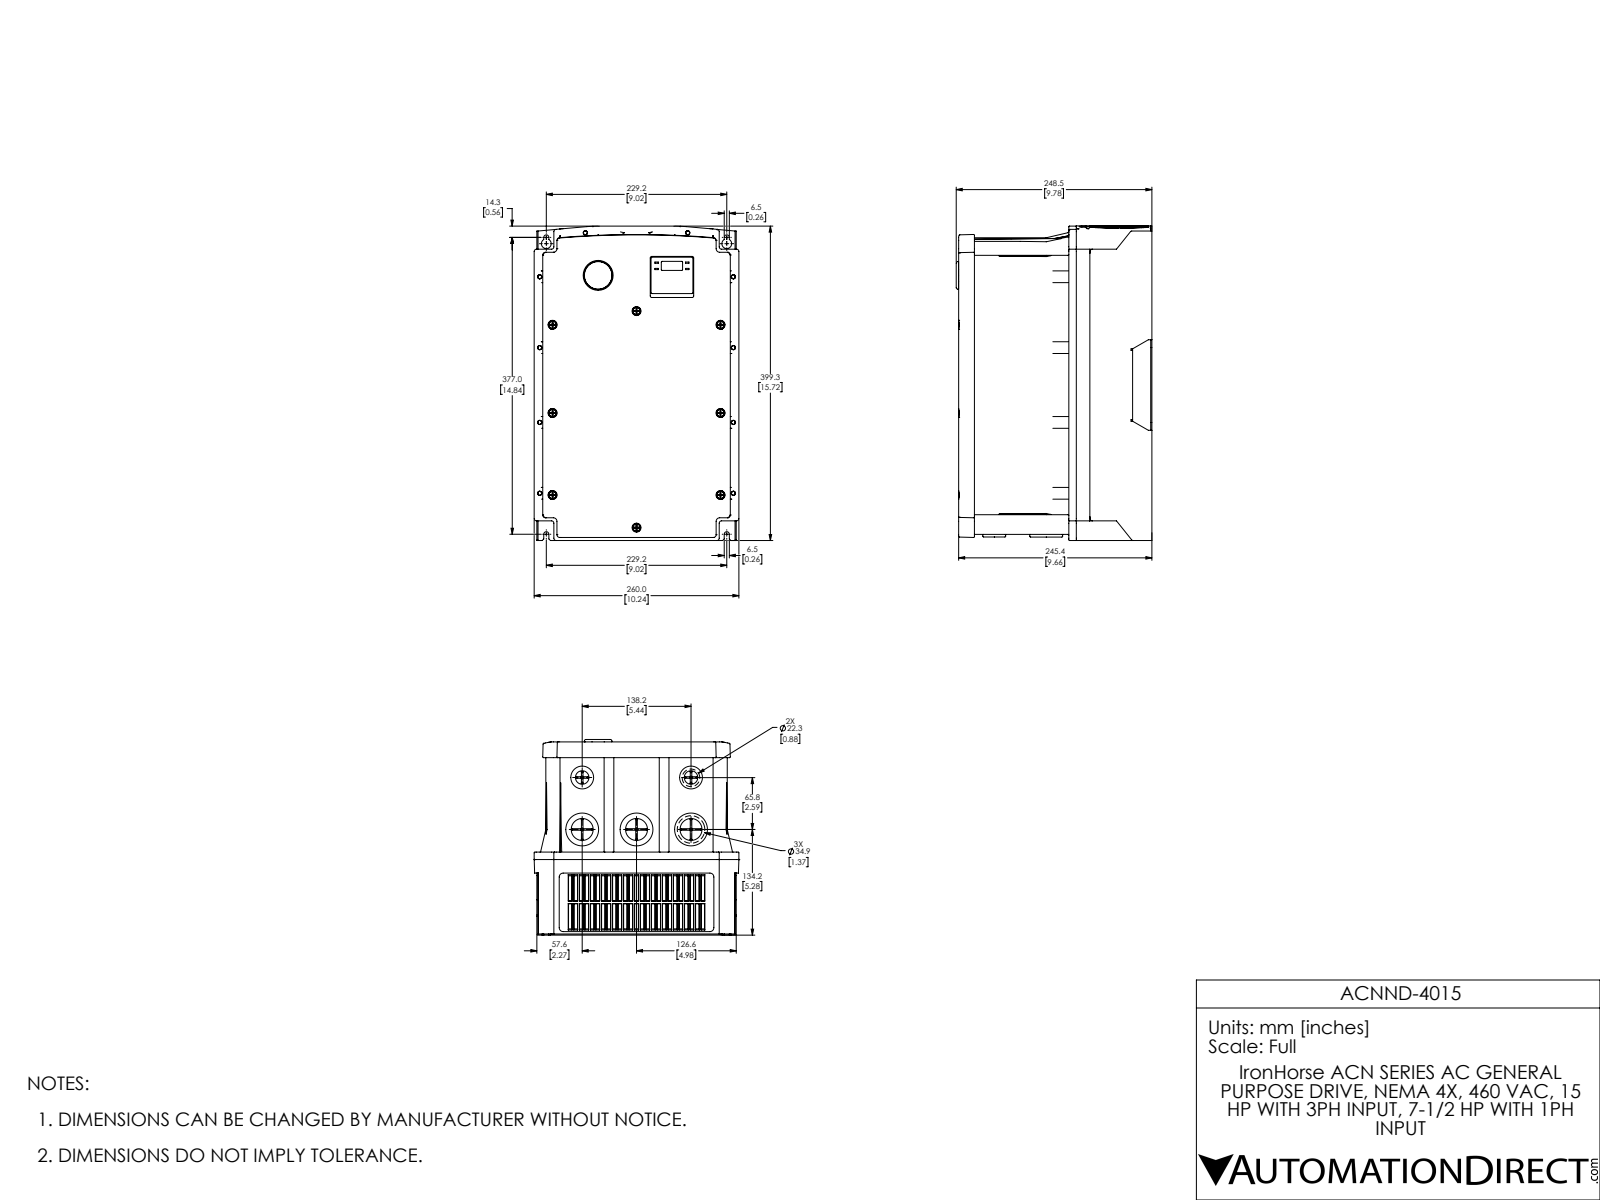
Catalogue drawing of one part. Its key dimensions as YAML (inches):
part_name: "total_s100_ip66_110_150_v3_asm red 1ext RED2 NEW1b2 COMPLETE EXT2F2 fill WITH NONPDS KNOB cmb3b sm2 cmb r1"
step_written_by: "SolidWorks 2017 (AUTOMOTIVE_DESIGN)"
units: inches
bodies: {solids: 2, faces: 5255, planar: 2354, cylindrical: 1370, other: 1531}
overall_size: [15.732, 10.236, 9.783]
volume: 1323
surface_area: 1378
round_holes:
  - {diameter: 0.217, count: 12}
  - {diameter: 0.197, count: 11}
  - {diameter: 0.409, count: 8}
  - {diameter: 1.098, count: 3}
  - {diameter: 1.524, count: 3}
  - {diameter: 0.492, count: 2}
  - {diameter: 0.677, count: 2}
  - {diameter: 0.878, count: 2}
  - {diameter: 1.024, count: 2}
  - {diameter: 1.181, count: 2}
  - {diameter: 1.772, count: 2}
  - {diameter: 2.362, count: 2}
round_bosses_or_shafts:
  - {diameter: 0.394, count: 8}
  - {diameter: 1.642, count: 3}
  - {diameter: 1.35, count: 3}
  - {diameter: 2.559, count: 2}
  - {diameter: 1.969, count: 2}
  - {diameter: 1.378, count: 2}
  - {diameter: 1.142, count: 2}
  - {diameter: 0.85, count: 2}
partial_cylinders:
  - {radius: 0.039, count: 127}
  - {radius: 0.012, count: 91}
  - {radius: 0.02, count: 85}
  - {radius: 0.008, count: 65}
  - {radius: 0.031, count: 36}
  - {radius: 0.118, count: 34}
  - {radius: 0.197, count: 25}
  - {radius: 0.157, count: 20}
face_to_face_distances: [0.059, 9.661, 9.461, 0.449, 9.52, 9.909, 0.39, 9.602, 9.071, 9.85]
hole_center_spacings: [3.543, 4.067, 5.138, 7.283, 9.685, 10.313, 12.118, 8.394]
